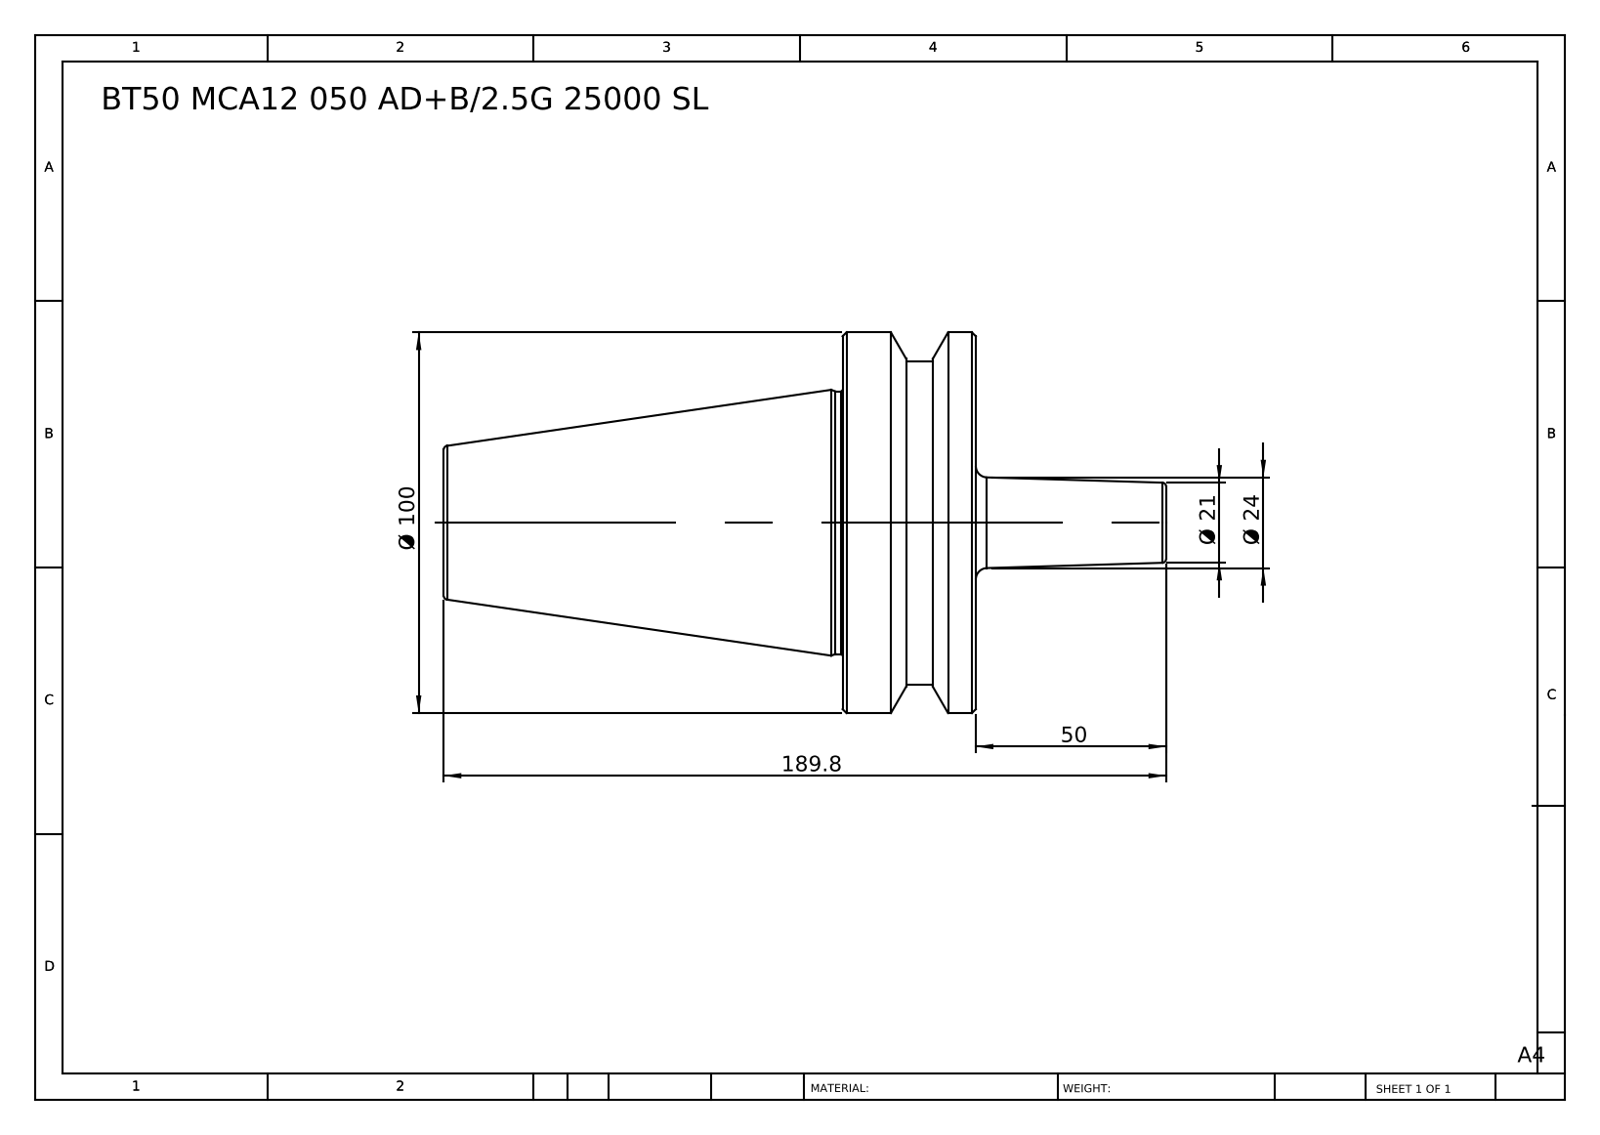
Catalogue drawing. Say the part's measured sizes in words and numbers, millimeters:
The part is named "BT50 MCA12 050 AD+B-2.5G 25000 SL". Its 3-D file was written by "SolidWorks 2014 (CONFIG_CONTROL_DESIGN)". It is 1 solid with 36 faces: 6 planar, 8 cylindrical and 22 other. Overall it measures 189.8 by 100 by 100 millimeters. Its volume is 530 091 cubic millimeters and its surface area 47 680 square millimeters. Round bosses or shafts: 1 of diameter 100, 1 of diameter 85, 1 of diameter 69. The main face-to-face distances are 35, 139.8, 104.8, 50, 85, 189.8, 61.3, 11.3, 23.7, 128.5.
